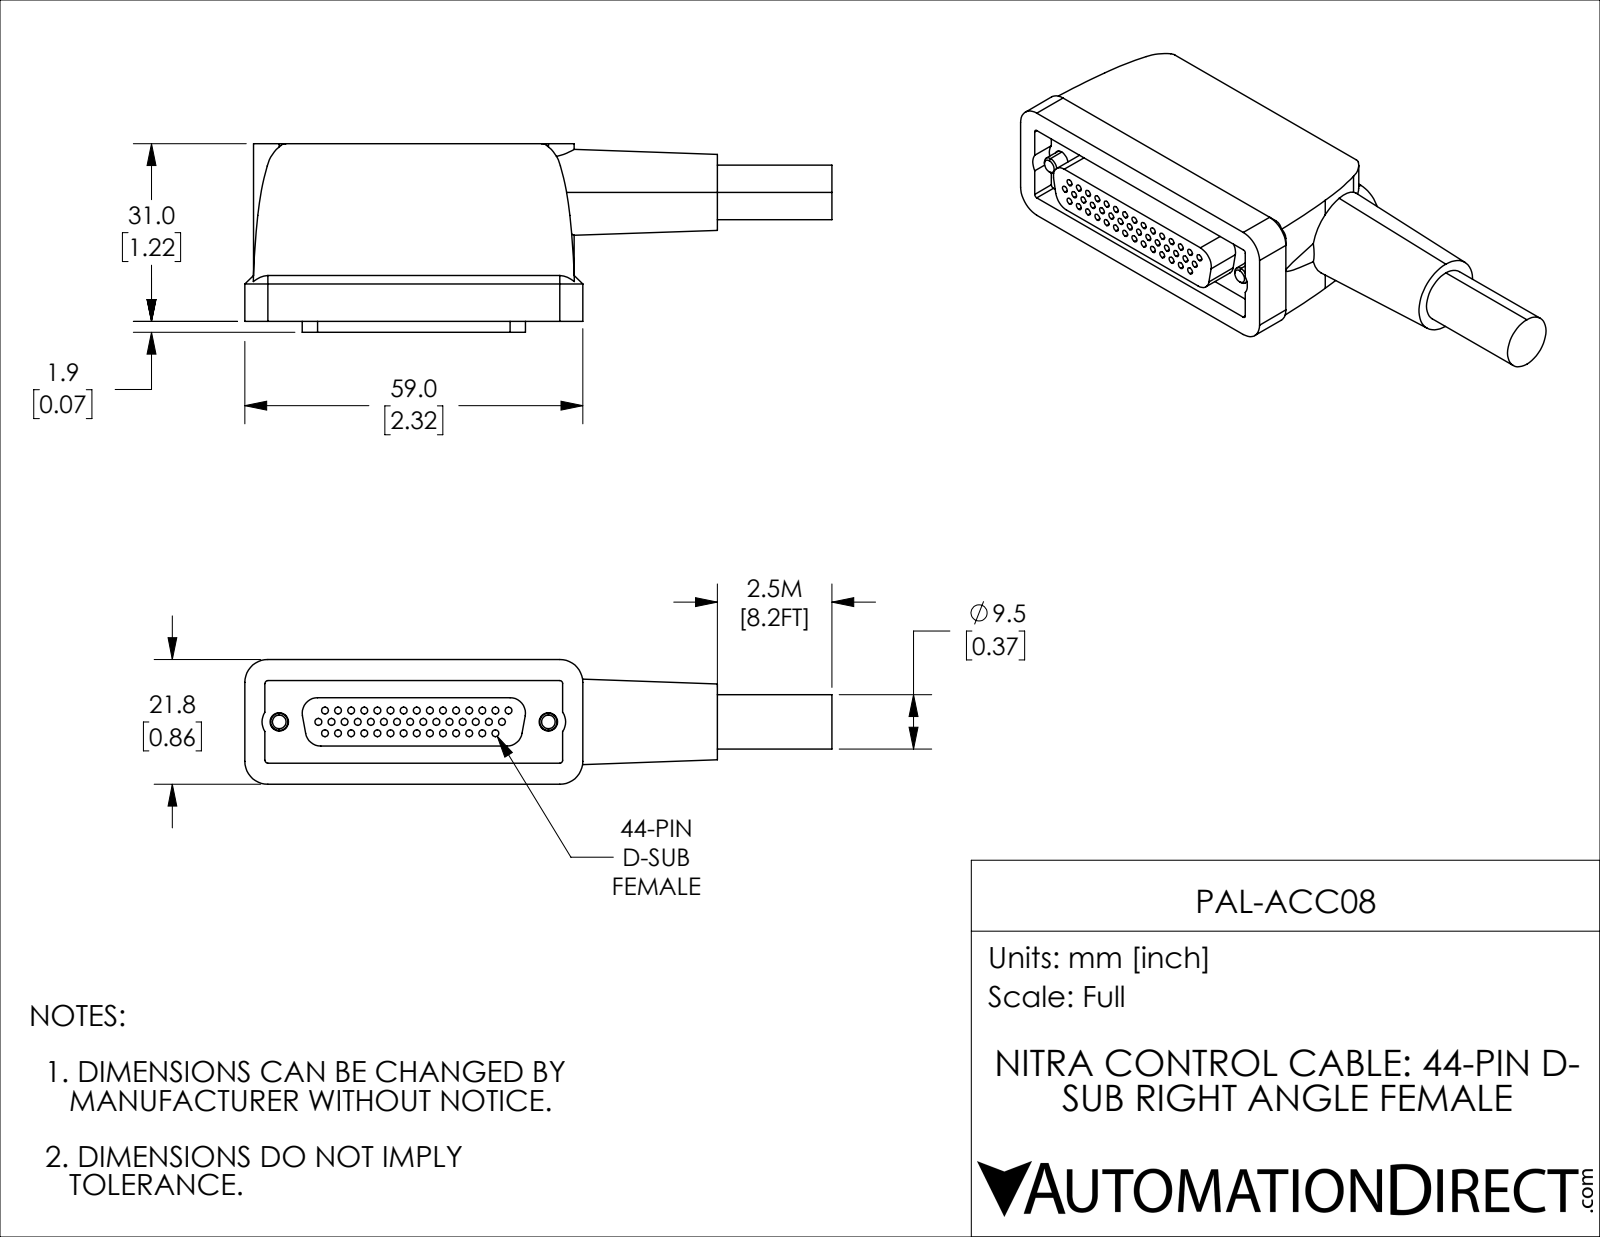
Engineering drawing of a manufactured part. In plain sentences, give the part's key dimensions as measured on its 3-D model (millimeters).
The part is named "PAL-ACC08". Its 3-D file was written by "SolidWorks 2019 (CONFIG_CONTROL_DESIGN)". It is 1 solid with 243 faces: 90 planar, 139 cylindrical and 14 other. Overall it measures 102.5 by 32.9 by 21.8 millimeters. Its volume is 37 413 cubic millimeters and its surface area 11 915 square millimeters. Round holes: 44 of diameter 1.2, 2 of diameter 3.2, 2 of diameter 5. Round bosses or shafts: 2 of diameter 4.6, 2 of diameter 3, 1 of diameter 9.5. Partial cylindrical surfaces (rounded edges, fillets, slot ends): 4 of radius 0.5, 4 of radius 2.68, 4 of radius 4, 2 of radius 1.4, 2 of radius 3, 2 of radius 4.5, 2 of radius 6.5, 2 of radius 50. The main face-to-face distances are 18.8, 1.5, 20.3, 31, 4.1, 26.9, 3.7, 18.1, 2.2, 16.6. The hole center spacings are 2.29, 6.05, 3.96, 4.58, 6.87, 2.28, 3.97, 4.57.
